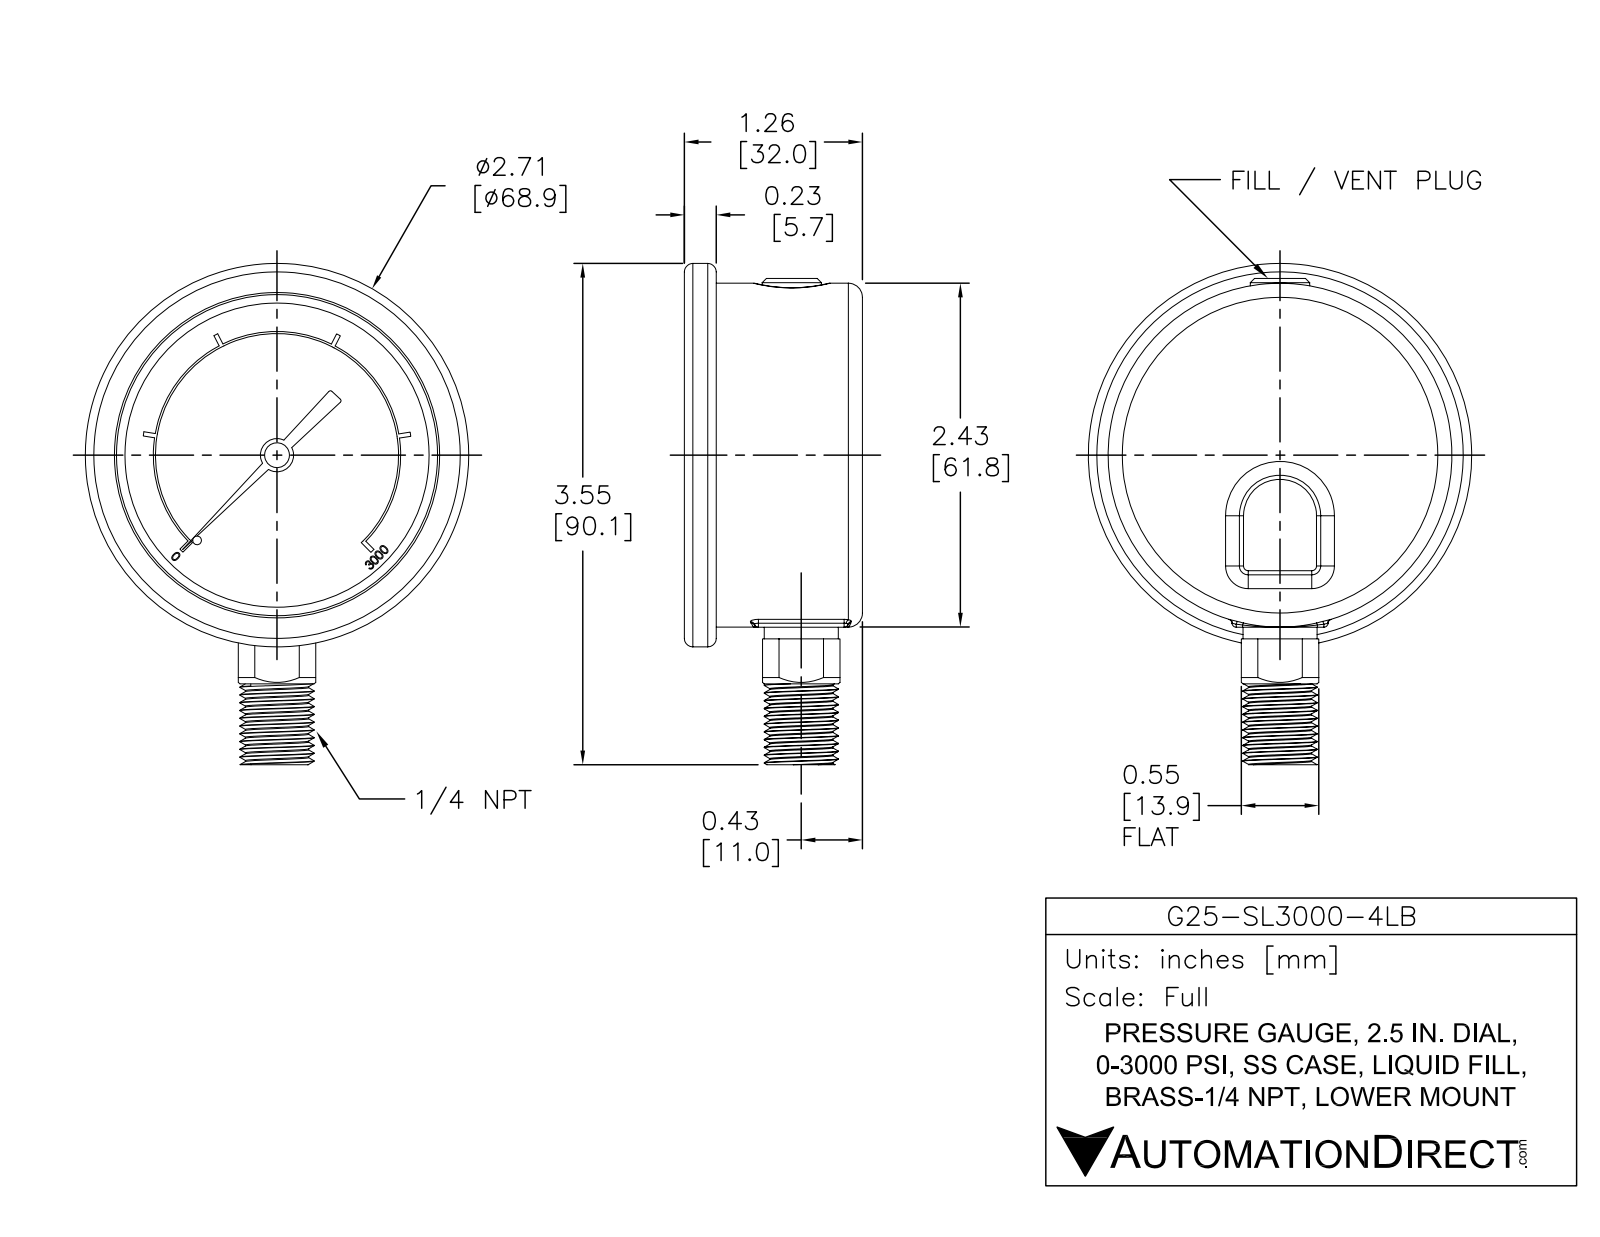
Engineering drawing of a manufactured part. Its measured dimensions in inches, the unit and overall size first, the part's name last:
Units: inches
Overall size (bounding box): 3.546 × 2.713 × 1.26
Round holes (diameter × count): ⌀0.027 ×1, ⌀0.071 ×1, ⌀0.119 ×1, ⌀2.272 ×1
Round bosses / shafts (diameter × count): ⌀2.713 ×1, ⌀2.433 ×1, ⌀0.524 ×1, ⌀0.42 ×1, ⌀0.235 ×1, ⌀0.176 ×1, ⌀0.14 ×1, ⌀0.041 ×1
Partial cylindrical surfaces — rounded edges, fillets, slot ends (radius × count): R0.03 ×9, R0.1 ×3, R0.015 ×2, R0.316 ×1, R0.86 ×1, R0.875 ×1
Main face-to-face distances: 1.01, 1.26, 0.25, 1.035, 0.025, 0.225, 0.1, 0.91, 0.935, 1.16
Hole centre spacings: 0.067
Volume: 5.273 in³ · Surface area: 24.68 in²
Bodies: 1 solid, 365 faces (194 planar, 85 cylindrical, 86 other)
Part name (STEP PRODUCT): G25-SL3000-4LB
STEP written by: SolidWorks 2021 (AUTOMOTIVE_DESIGN)
